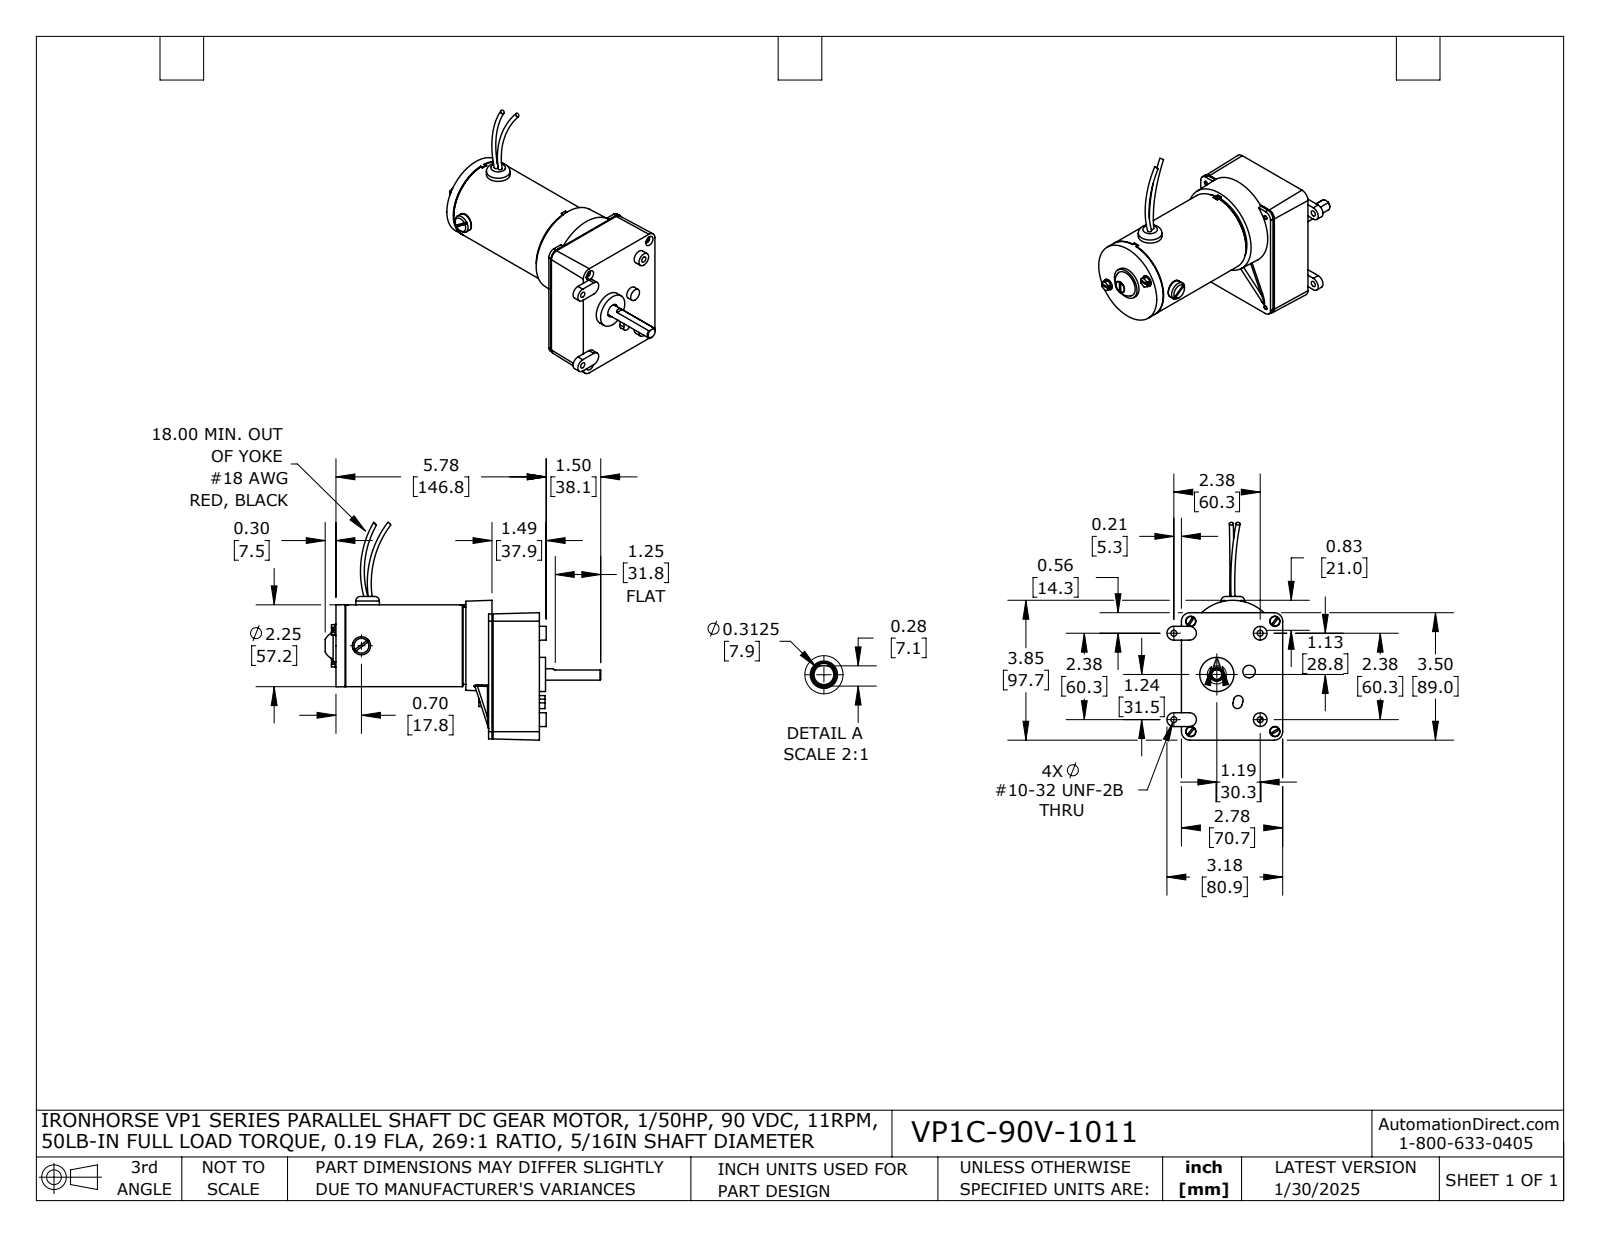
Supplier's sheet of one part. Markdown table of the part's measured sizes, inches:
| quantity | value |
| --- | --- |
| part name | VP1C-90V-1011 |
| STEP written by | SolidWorks 2021 (AUTOMOTIVE_DESIGN) |
| units | inches |
| bodies | 34 solids, 1338 faces (477 planar, 580 cylindrical, 281 other) |
| overall size | 7.578 × 5.989 × 3.183 |
| volume | 13.71 in³ |
| surface area | 226.6 in² |
| round holes (diameter × count) | 0.281 × 7, 0.037 × 4, 0.117 × 4, 0.149 × 4, 0.15 × 4, 0.161 × 4, 0.125 × 2, 0.187 × 2, 0.127 × 1, 0.127 × 1, 0.213 × 1, 0.239 × 1 |
| round bosses / shafts (diameter × count) | 0.136 × 4, 0.313 × 3, 0.375 × 2, 2.256 × 1, 2.25 × 1, 2.123 × 1, 2.003 × 1, 2 × 1 |
| partial cylindrical surfaces (radius × count) | 0.028 × 24, 0.051 × 24, 0.02 × 12, 0.055 × 12, 0.058 × 12, 0.03 × 8, 0.031 × 8, 0.19 × 8 |
| main face-to-face distances | 1.304, 0.097, 1.207, 1.397, 1.3, 0.093, 1.273, 1.176, 0.031, 0.124 |
| hole center spacings | 0.875, 0.77, 1.936, 2.31, 2.312, 3.03, 3.031, 0.135 |
